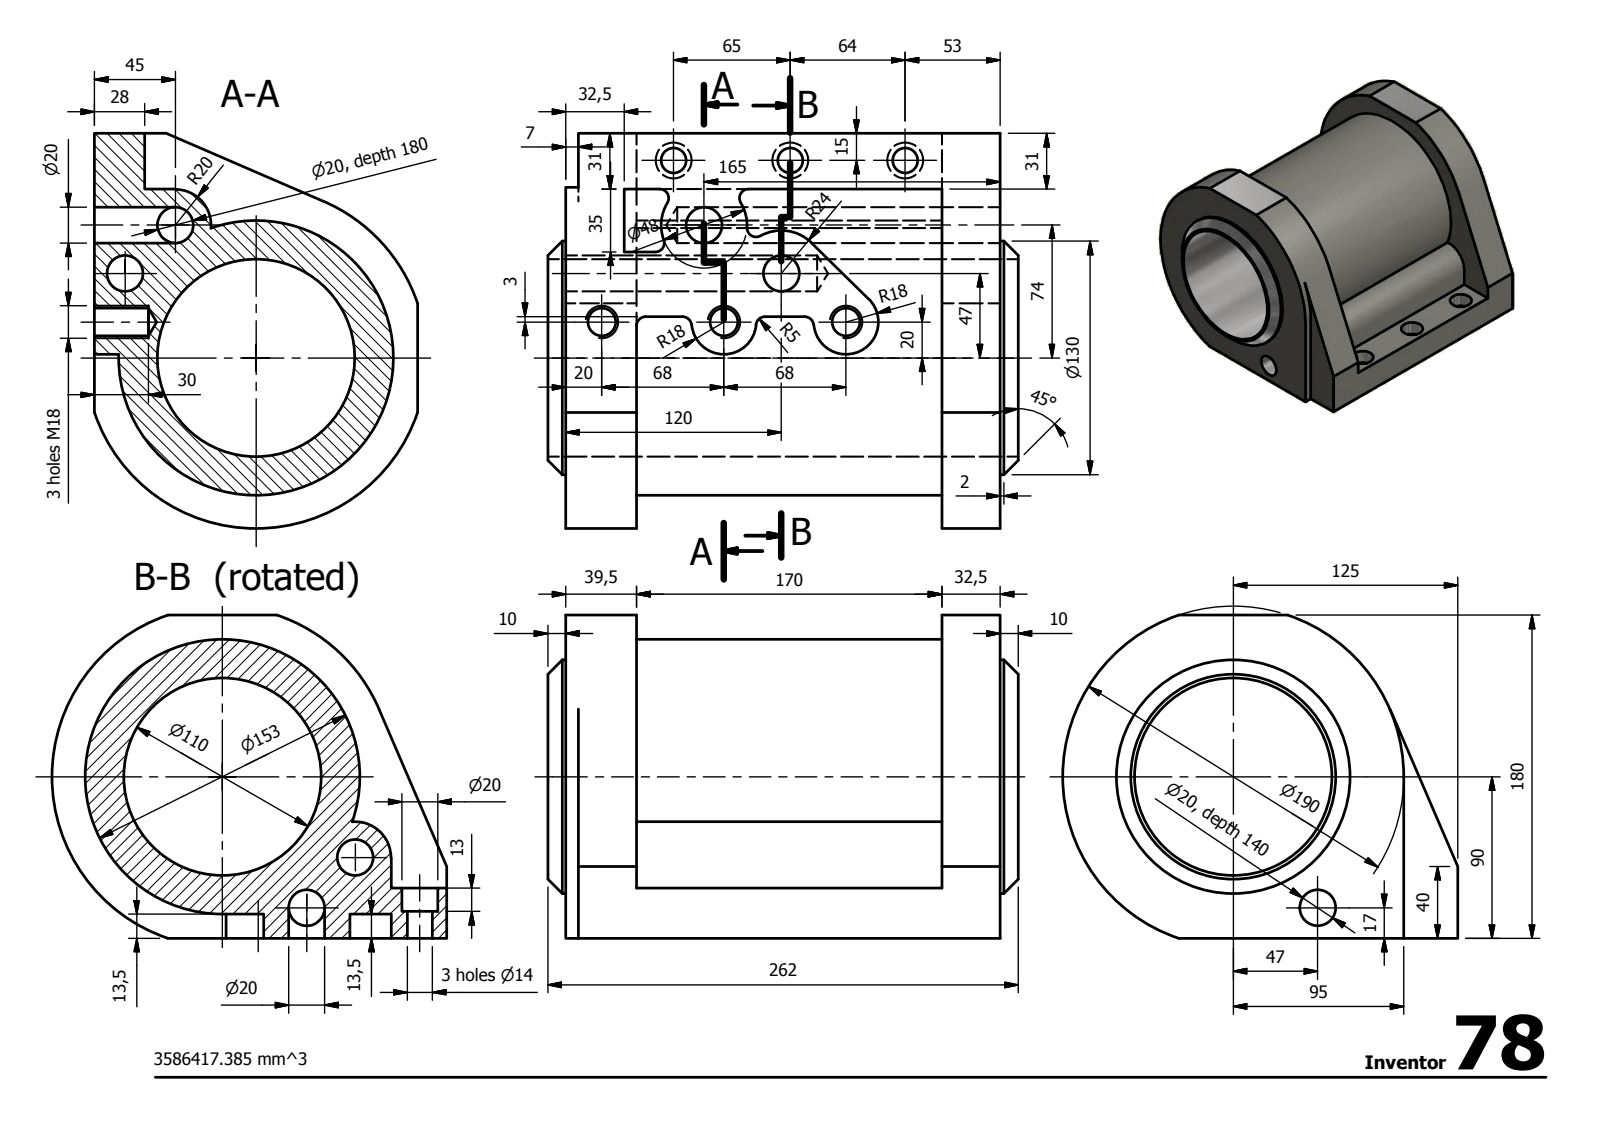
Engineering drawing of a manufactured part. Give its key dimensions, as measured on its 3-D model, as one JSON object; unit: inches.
{"step_written_by": "Autodesk Inventor 2014 (AUTOMOTIVE_DESIGN)", "units": "inches", "bodies": {"solids": 1, "faces": 70, "planar": 28, "cylindrical": 35, "other": 7}, "overall_size": [10.315, 8.661, 7.087], "volume_in3": 218.8, "surface_area_in2": 541.9, "round_holes": [[0.787, 7], [0.551, 3], [0.63, 3], [4.331, 1]], "round_bosses_or_shafts": [[6.024, 1], [5.118, 1]], "partial_cylinders_radius": [[0.197, 8], [0.709, 2], [0.945, 2], [0.787, 1], [3.74, 1]], "face_to_face_distances": [9.528, 1.28, 7.972, 8.248, 1.555, 6.693, 0.531, 1.22, 7.087, 6.555], "hole_center_spacings": [2.677, 1.531, 1.567, 1.648, 1.772, 1.999, 2.17, 2.362]}
